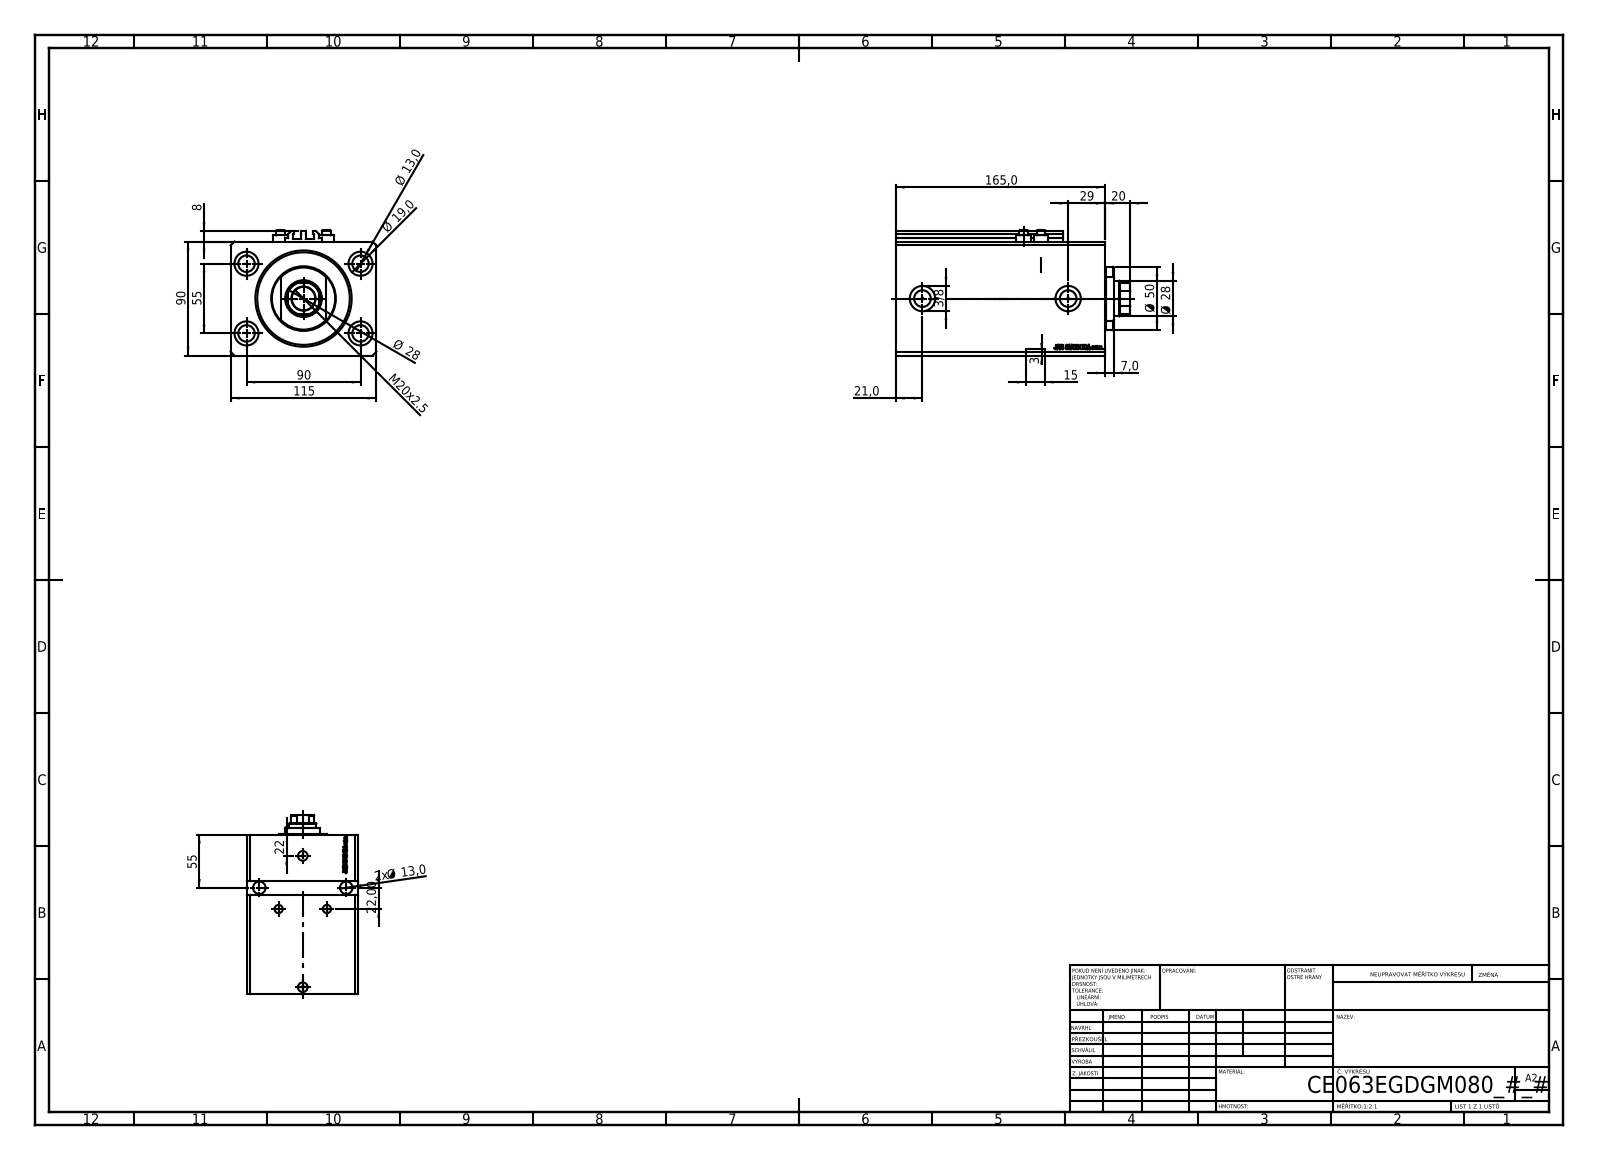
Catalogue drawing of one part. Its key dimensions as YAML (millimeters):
part_name: "V250CE_VC_E; V250CE_C_VCP; ALLEN BOLT V250CE; V250CE_E_Body"
step_written_by: "SolidWorks 2019 (CONFIG_CONTROL_DESIGN)"
units: millimeters
bodies: {solids: 8, faces: 1131, planar: 547, cylindrical: 146, other: 438}
overall_size: [185, 115, 99]
volume: 1391000
surface_area: 214532
round_holes:
  - {diameter: 13, count: 6}
  - {diameter: 1.25, count: 4}
  - {diameter: 4, count: 4}
  - {diameter: 19, count: 4}
  - {diameter: 8.5, count: 2}
  - {diameter: 10, count: 2}
  - {diameter: 13.16, count: 2}
  - {diameter: 20, count: 2}
  - {diameter: 18.5, count: 1}
  - {diameter: 28, count: 1}
  - {diameter: 63, count: 1}
  - {diameter: 76, count: 1}
round_bosses_or_shafts:
  - {diameter: 11.6, count: 4}
  - {diameter: 7, count: 4}
  - {diameter: 50, count: 1}
partial_cylinders:
  - {radius: 0.2, count: 10}
  - {radius: 13.5, count: 1}
face_to_face_distances: [90, 115, 165, 20, 17.9, 147.1, 145, 127.1, 65, 80]
hole_center_spacings: [52.74, 90, 13.6, 14.76, 27.39, 27.51, 28.46, 29.73]
